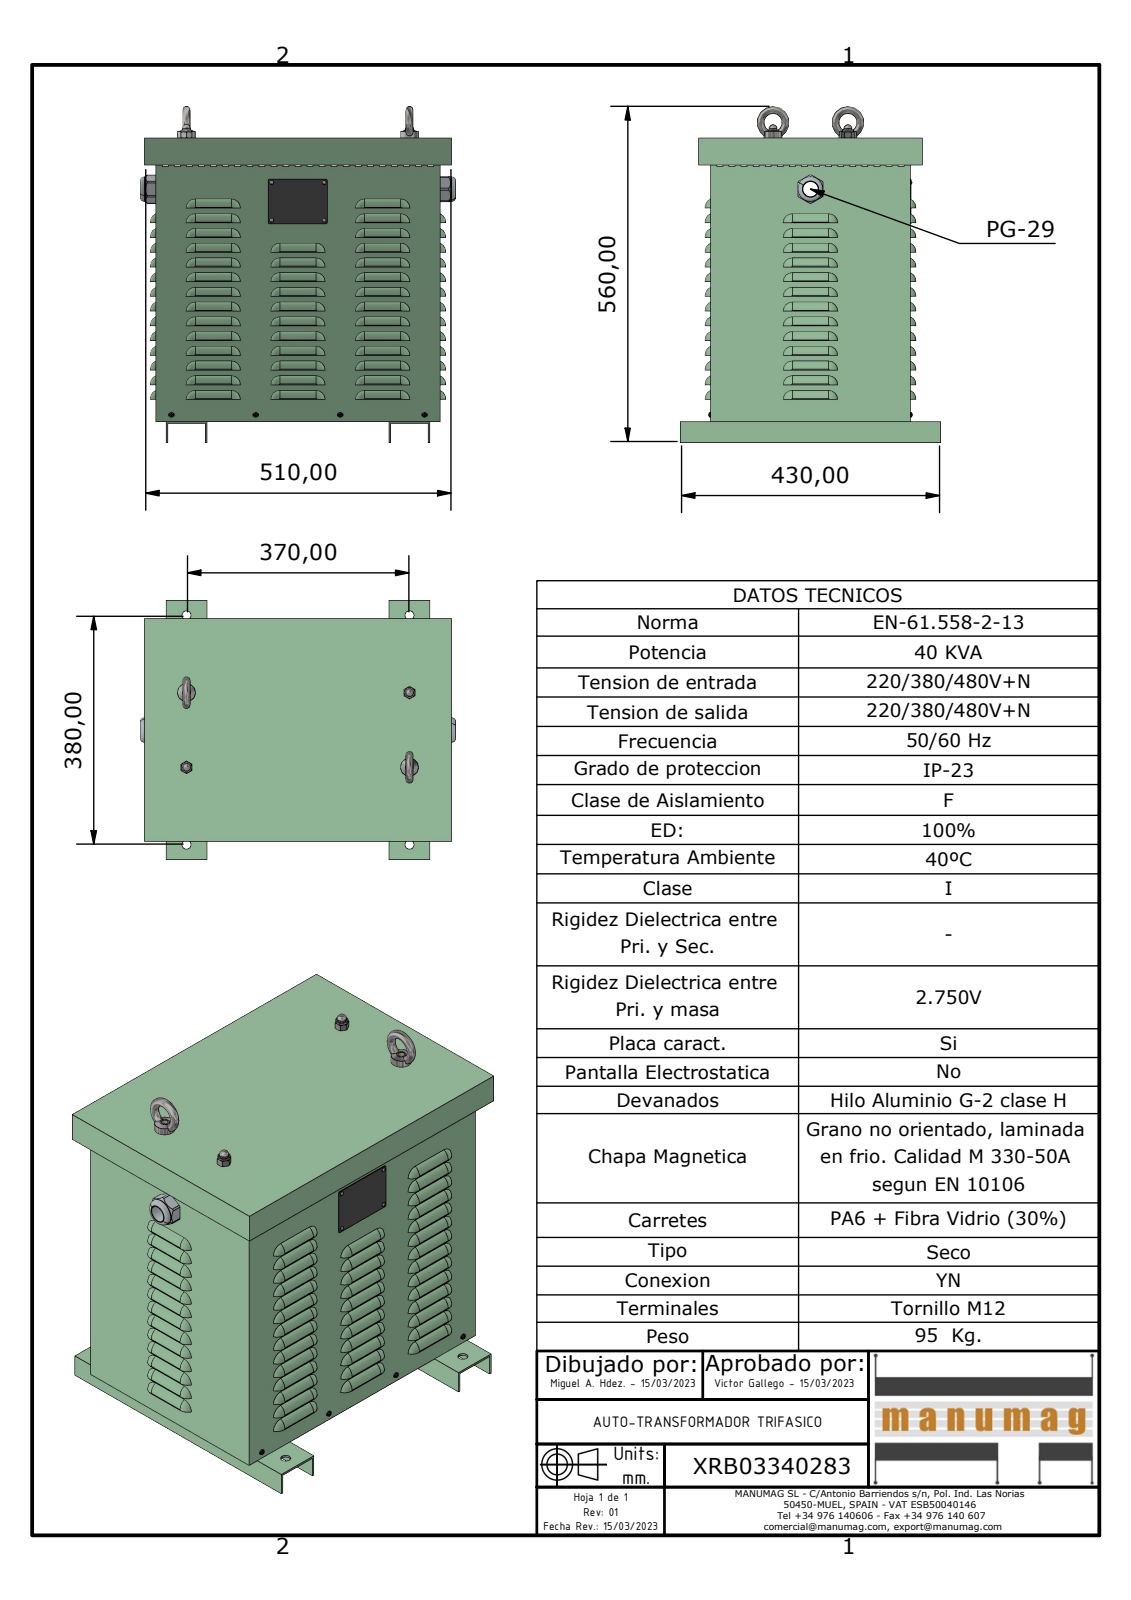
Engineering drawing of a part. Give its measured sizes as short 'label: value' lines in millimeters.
name: XRB03340283; JE040 - JE050 CUERPO; JE040 - JE050 BASE; JE040 - JE050 PATAS (+7 more)
written by: Autodesk Inventor 2023 (AUTOMOTIVE_DESIGN)
unit: mm
bodies: 24 solids, 2403 faces (969 planar, 808 cylindrical, 626 other)
size: 560 × 523.4 × 431
volume: 3 115 000 mm³; area: 2 768 000 mm²
holes: 260× ⌀11, 4× ⌀4, 4× ⌀5, 4× ⌀10.11, 4× ⌀14, 4× ⌀15, 1× ⌀25, 1× ⌀38
bosses: 4× ⌀4, 4× ⌀3.62, 4× ⌀3.2, 2× ⌀30, 2× ⌀18, 2× ⌀13.6, 1× ⌀40.8, 1× ⌀37.3
rounds: 104× R14, 54× R7, 54× R15, 12× R3.22, 8× R2.5, 8× R7.5, 4× R2, 1× R23.85
face distances: 2, 470, 472, 329, 468, 327, 331, 3, 19.5, 348.5
hole spacings: 31.76, 71.59, 15, 28, 70, 44.6, 99.14, 140.8
